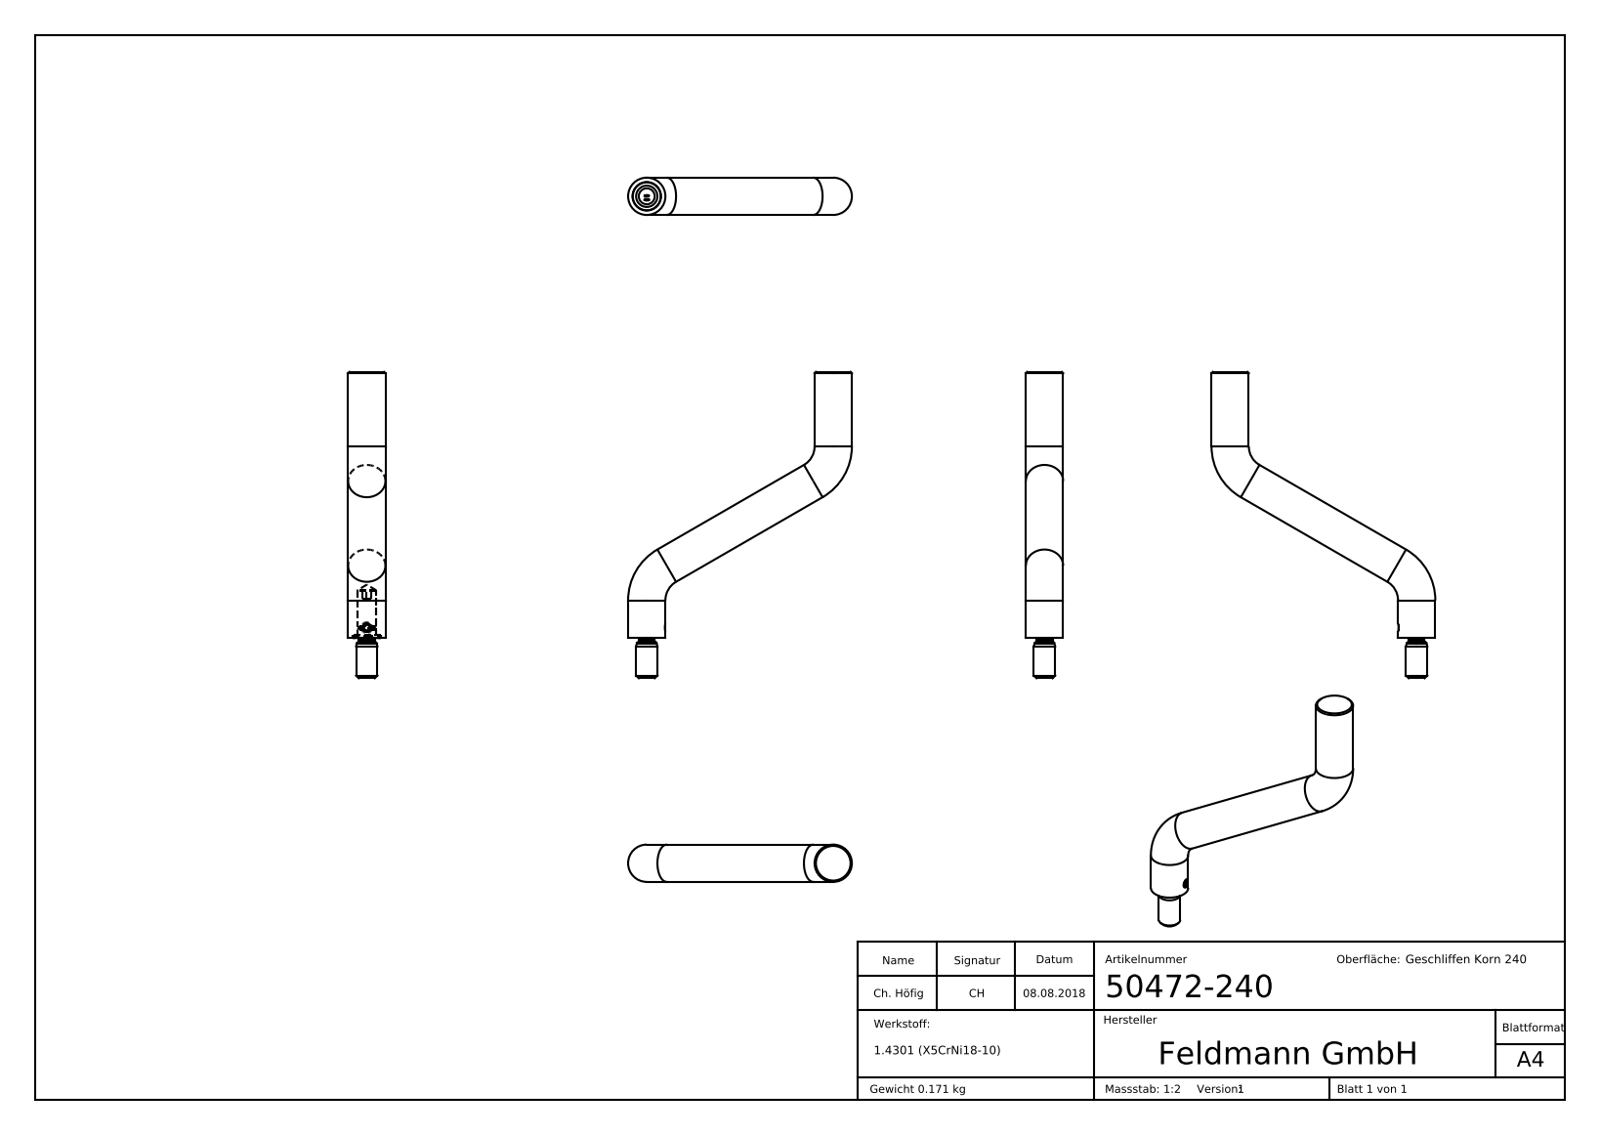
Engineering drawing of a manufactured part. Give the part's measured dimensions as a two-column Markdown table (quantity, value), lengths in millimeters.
| quantity | value |
| --- | --- |
| part name | DIN 914_-_M04 x 04_DIN 914 M4 x 4; 50472-240 Teil2_50472-240 Teil2; 50472-240; 50472-240 Teil1_50472-240 Teil1 |
| STEP written by | SolidWorks 2015 (CONFIG_CONTROL_DESIGN) |
| units | millimeters |
| bodies | 3 solids, 304 faces (158 planar, 24 cylindrical, 122 other) |
| overall size | 115 × 84 × 14 |
| volume | 21 704 mm³ |
| surface area | 7 840 mm² |
| round holes (diameter × count) | 3.3 × 1, 7.1 × 1, 10.7 × 1 |
| round bosses / shafts (diameter × count) | 14 × 3, 10.5 × 1, 8 × 1, 7 × 1, 6 × 1, 4 × 1 |
| main face-to-face distances | 100, 1.2, 98.8, 1, 99, 15, 16, 16.2, 115, 33 |
